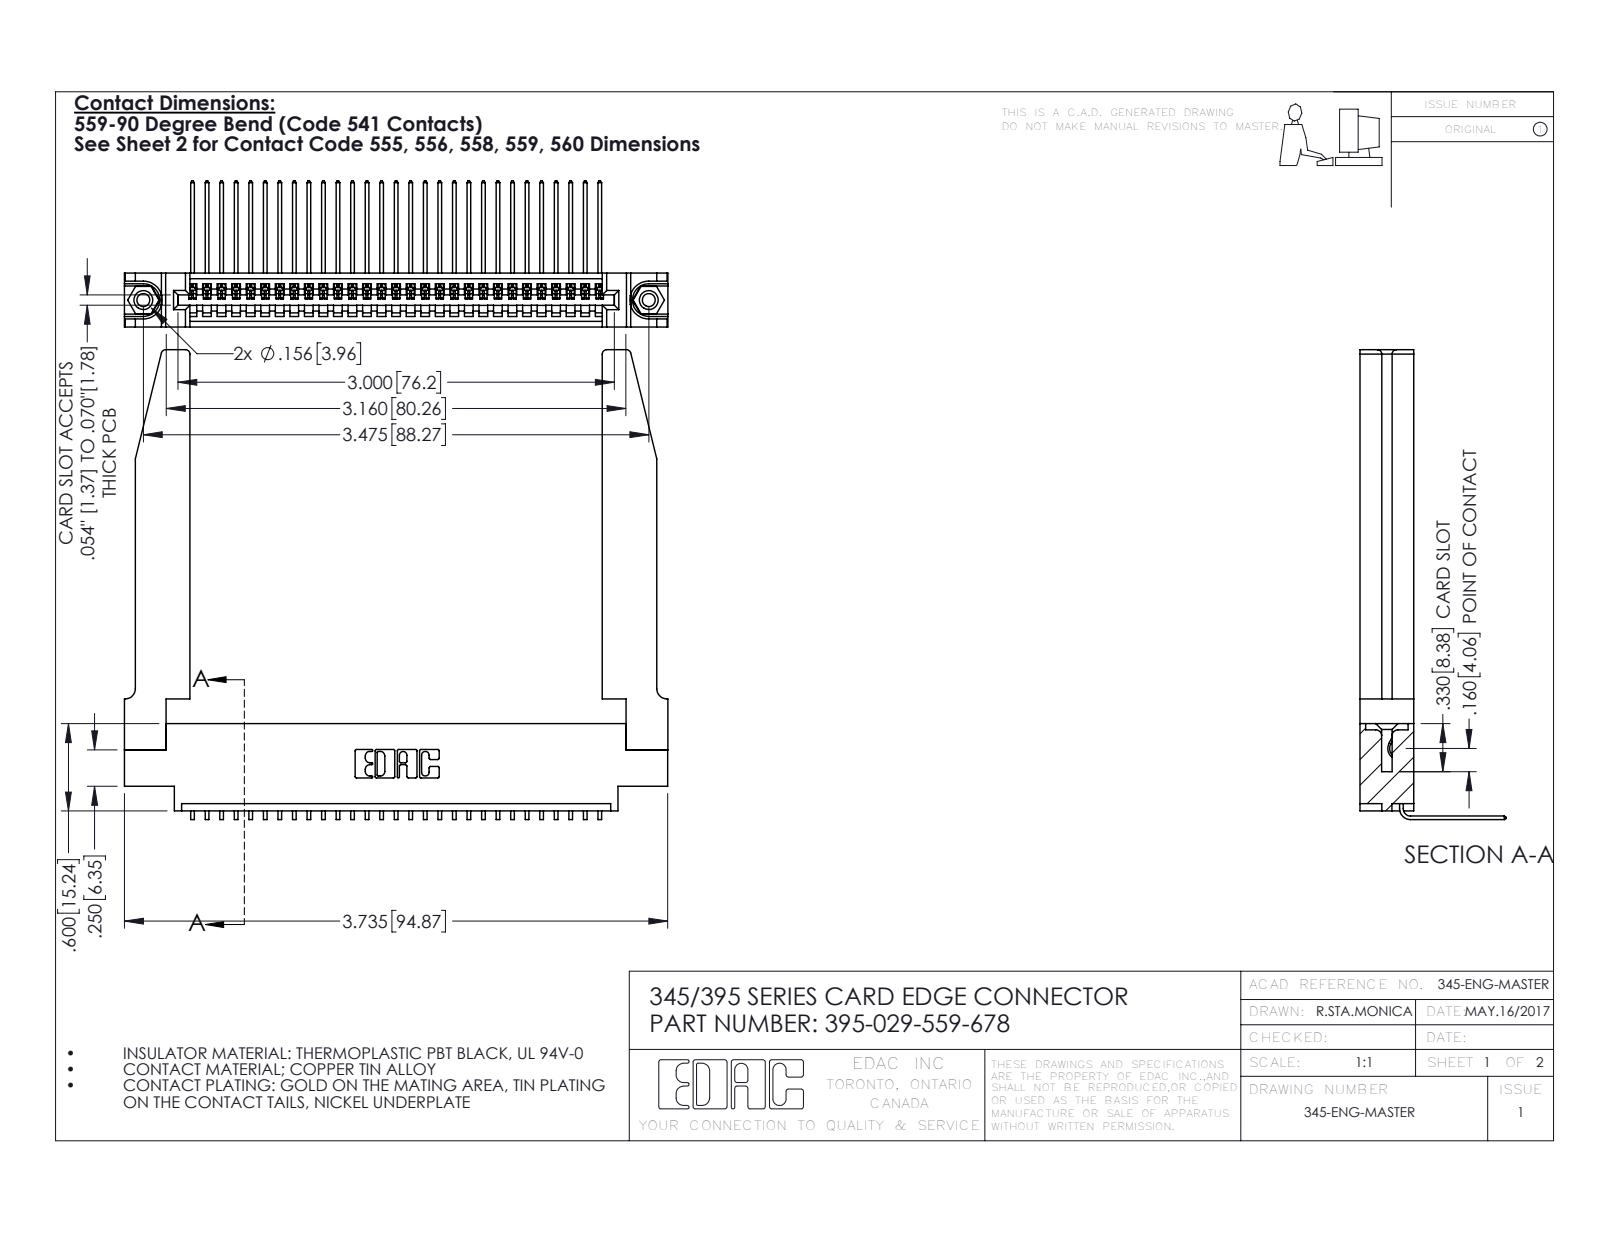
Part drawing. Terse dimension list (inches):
name: 345-250-001_345-250-001-102; 395-029-559-678; 345-220-078_345-220-078; 345-292-001_558 559 Tail - 1 (+1 more)
written by: SolidWorks 2016 (CONFIG_CONTROL_DESIGN)
unit: in
bodies: 34 solids, 2104 faces (1444 planar, 608 cylindrical, 52 other)
size: 3.736 × 3.229 × 1.005
volume: 1.017 in³; area: 29.72 in²
holes: 2× ⌀0.089, 2× ⌀0.125, 2× ⌀0.156, 1× ⌀0.064
bosses: 2× ⌀0.155
rounds: 58× R0.006, 22× R0.01, 8× R0.03, 6× R0.007, 6× R0.031, 3× R0.026, 2× R0.031, 2× R0.04
face distances: 0.37, 0.072, 0.298, 0.098, 0.272, 0.025, 0.2, 0.148, 0.15, 0.225
hole spacings: 0.27, 3.24, 3.475
